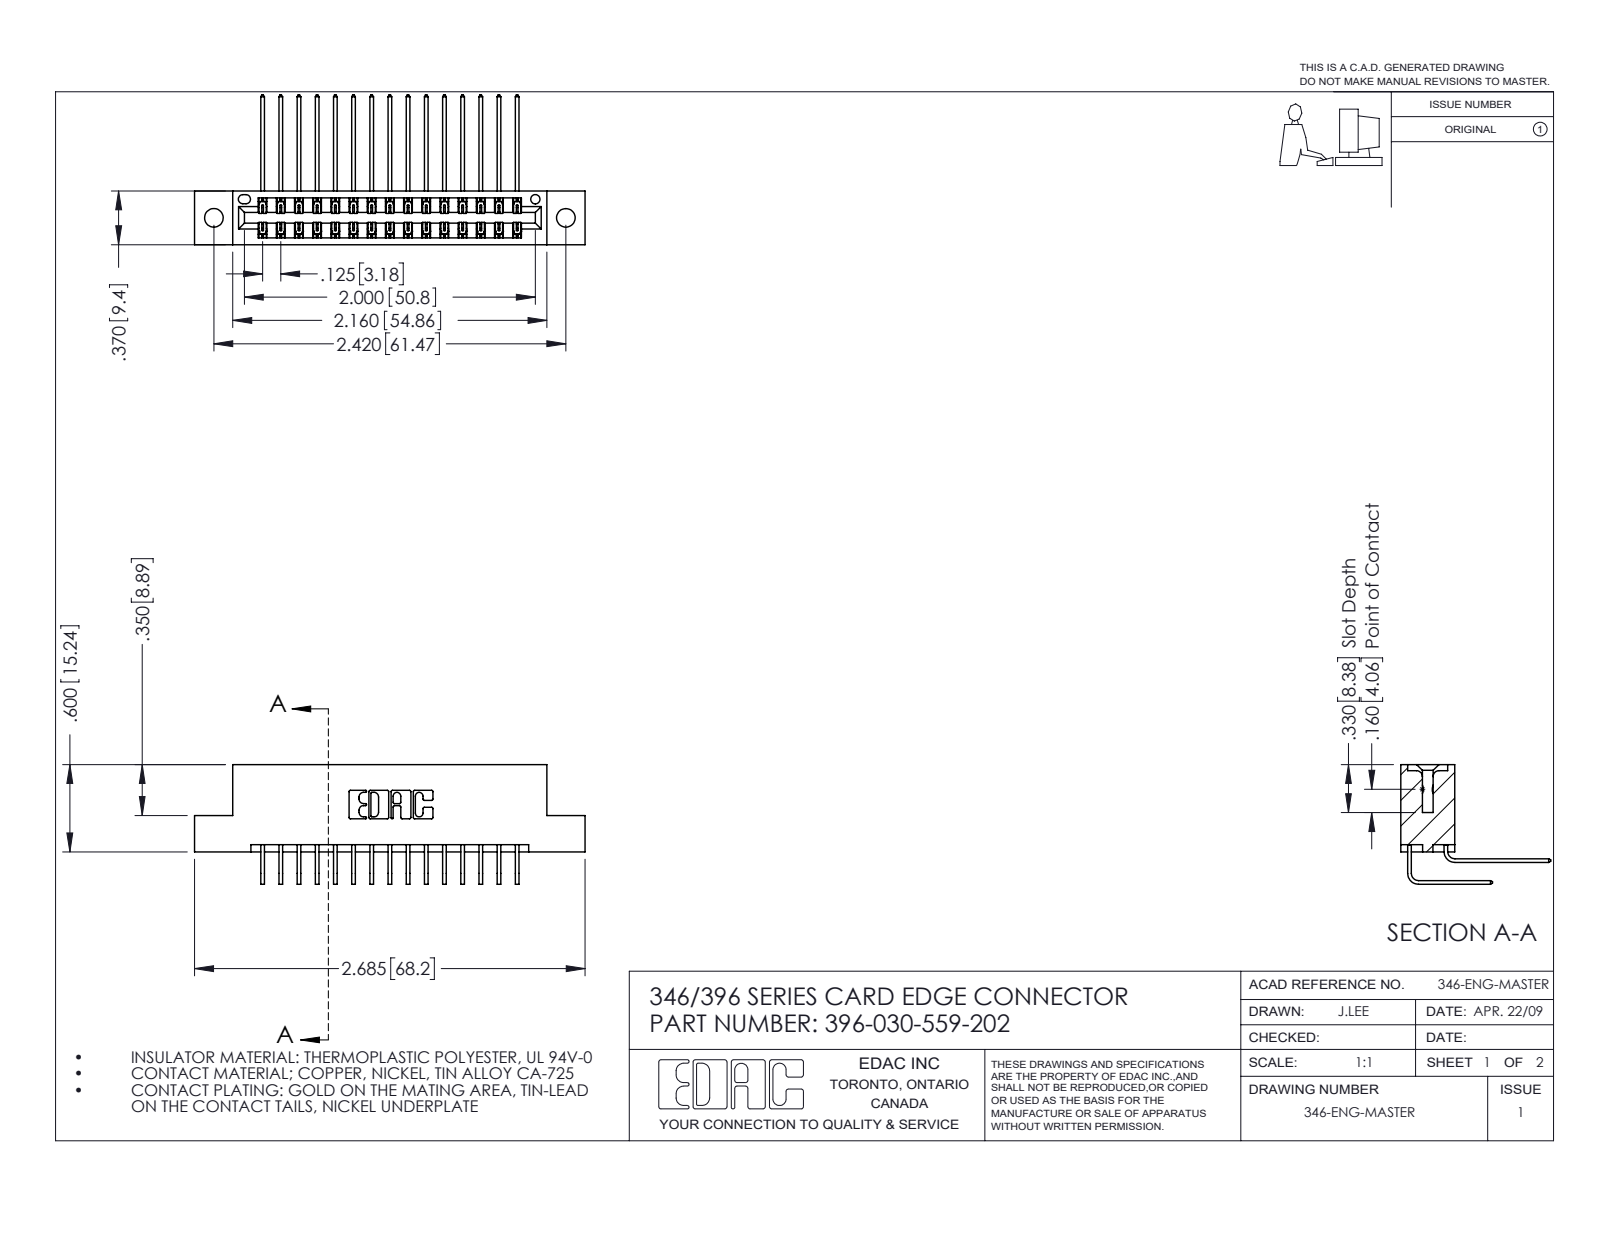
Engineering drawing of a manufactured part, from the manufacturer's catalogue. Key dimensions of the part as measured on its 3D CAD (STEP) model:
Part name (STEP PRODUCT): 345-292-001_559 Tail - 2; 345-292-001_558 559 Tail - 1; 396-030-559-202; 346 Part_Flush Mounting Lugs - 0.128 Dia
STEP written by: SolidWorks 2016 (CONFIG_CONTROL_DESIGN)
Units: inches
Bodies: 31 solids, 1742 faces (1186 planar, 556 cylindrical, 0 other)
Overall size (bounding box): 2.685 × 1.03 × 0.823
Volume: 0.401 in³ · Surface area: 14.22 in²
Round holes (diameter × count): ⌀0.128 ×2, ⌀0.064 ×1
Partial cylindrical surfaces — rounded edges, fillets, slot ends (radius × count): R0.006 ×45, R0.01 ×22, R0.007 ×6, R0.031 ×6, R0.026 ×3, R0.014 ×2, R0.022 ×2, R0.024 ×2
Main face-to-face distances: 0.048, 0.322, 0.25, 0.025, 0.37, 0.072, 0.298, 0.275, 0.148, 0.222
Hole centre spacings: 0.246, 2.213, 2.42
